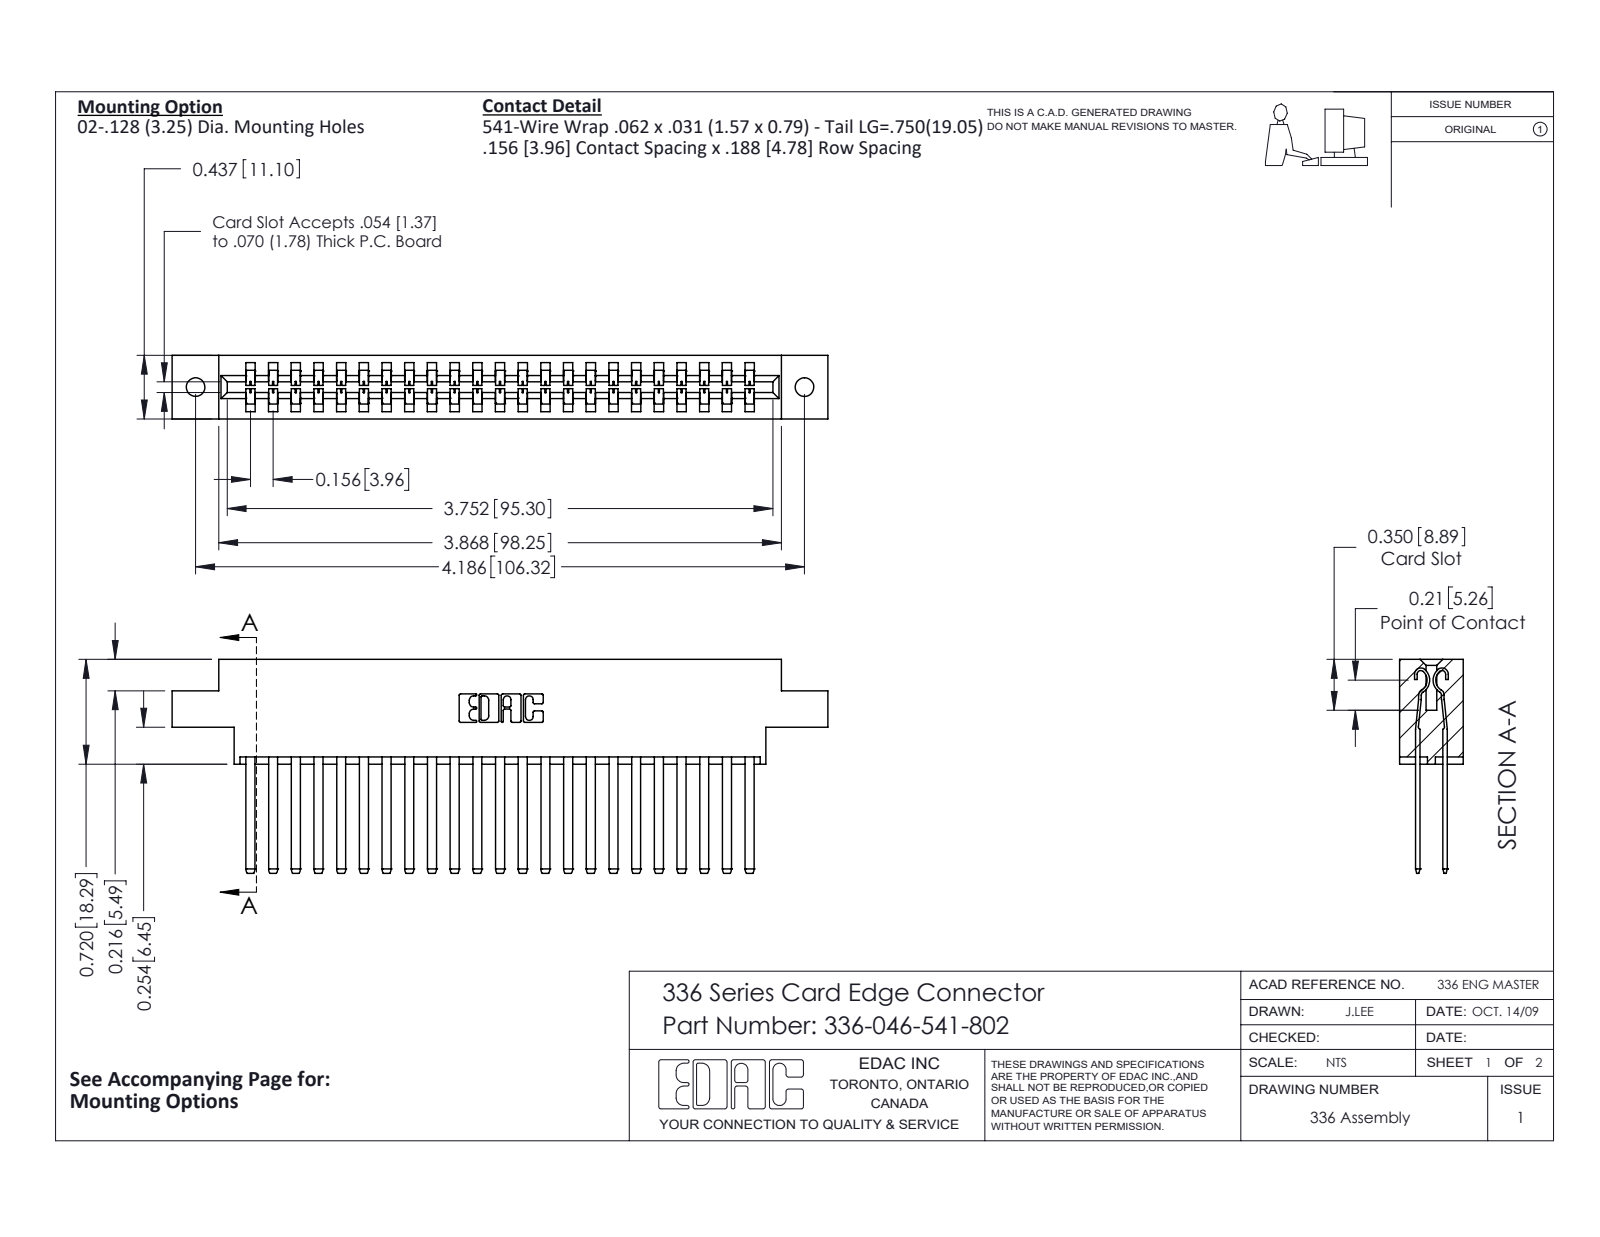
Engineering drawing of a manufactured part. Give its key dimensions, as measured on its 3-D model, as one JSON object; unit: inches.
{"part_name": "336-046-541-802; 336-290-001_336-290-541; 336 Part_Offset - .128 Dia", "step_written_by": "SolidWorks 2020 (CONFIG_CONTROL_DESIGN)", "units": "inches", "bodies": {"solids": 47, "faces": 2050, "planar": 1270, "cylindrical": 780, "other": 0}, "overall_size": [4.509, 1.47, 0.437], "volume_in3": 1.031, "surface_area_in2": 32.8, "round_holes": [[0.128, 2]], "partial_cylinders_radius": [[0.004, 92], [0.056, 46], [0.01, 22], [0.007, 6], [0.031, 6], [0.022, 4], [0.04, 4], [0.026, 3]], "face_to_face_distances": [0.188, 0.328, 0.14, 0.297, 0.109, 0.031, 0.437, 0.033, 0.156, 0.181], "hole_center_spacings": [4.186]}
